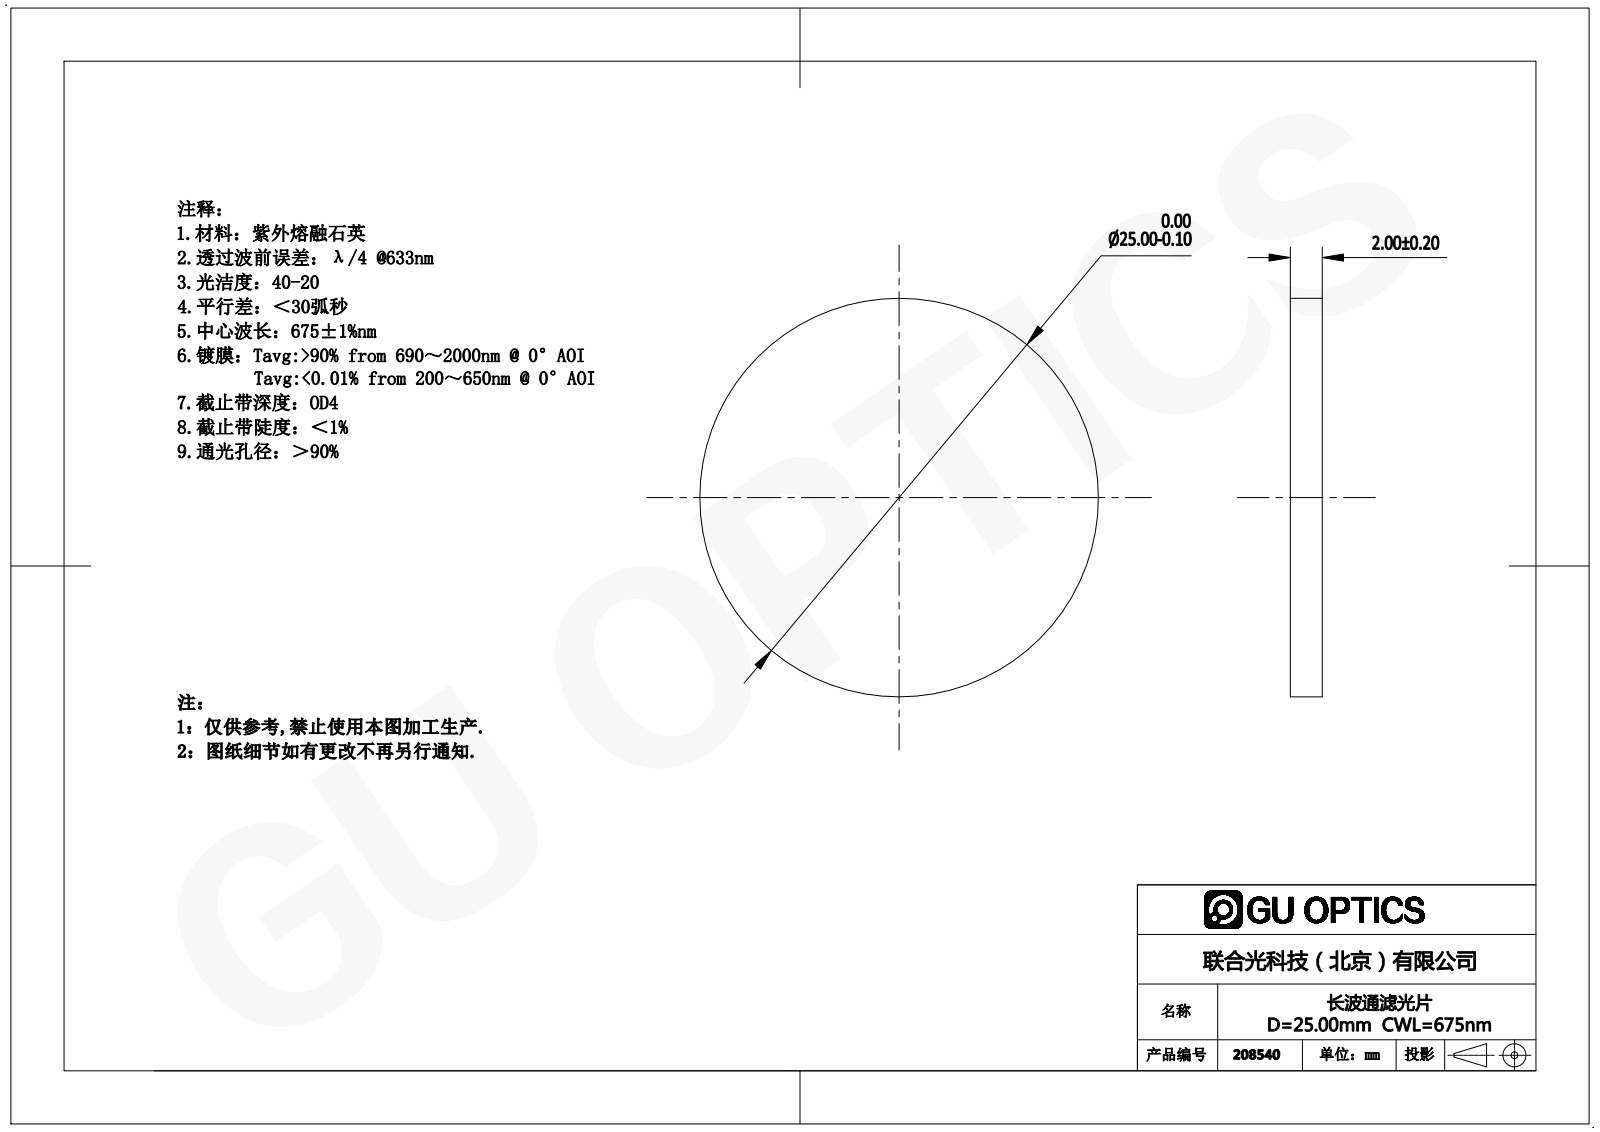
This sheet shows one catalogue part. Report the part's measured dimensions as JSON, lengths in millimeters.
{"part_name": "208529", "step_written_by": "SolidWorks 2016 (AUTOMOTIVE_DESIGN)", "units": "millimeters", "bodies": {"solids": 1, "faces": 4, "planar": 2, "cylindrical": 2, "other": 0}, "overall_size": [25, 25, 2], "volume_mm3": 982, "surface_area_mm2": 1139, "round_bosses_or_shafts": [[25, 1]], "face_to_face_distances": [2]}
